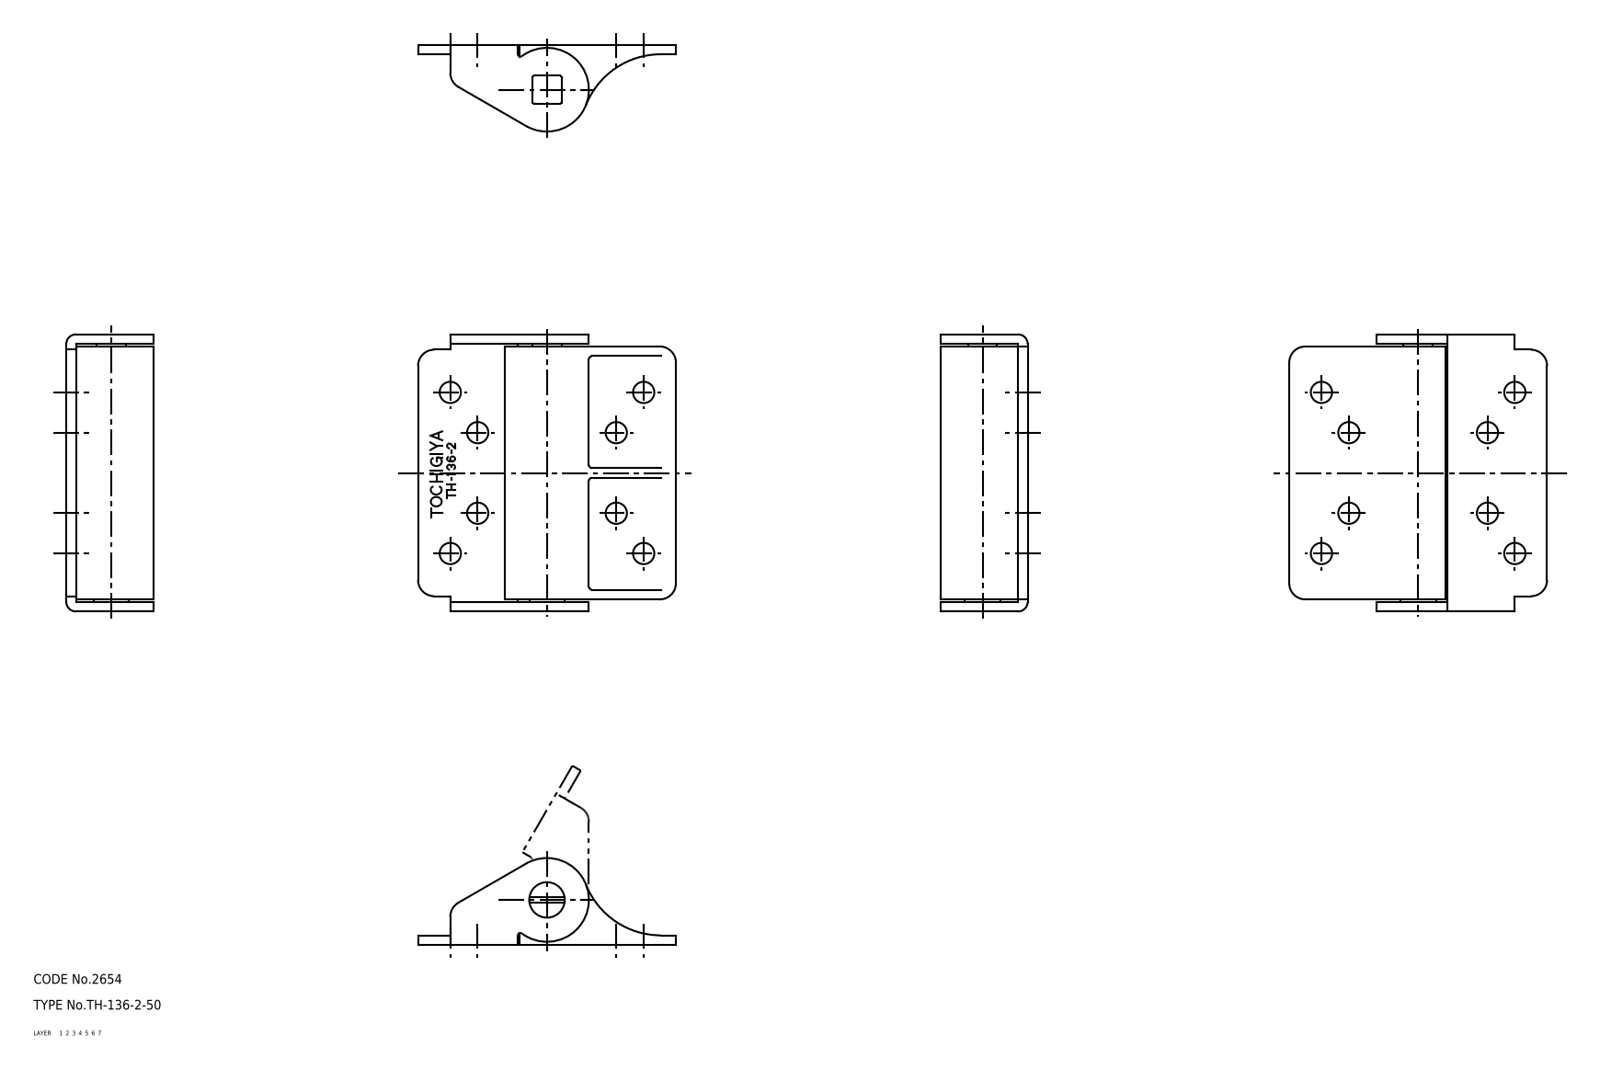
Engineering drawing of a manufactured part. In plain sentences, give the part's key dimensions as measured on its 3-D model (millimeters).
The part is named "hinge piece; needle; shaft; TH_136_2_50". Its 3-D file was written by "SolidWorks 2015 (AUTOMOTIVE_DESIGN)". It is 4 solids with 115 faces: 51 planar, 60 cylindrical and 4 other. Overall it measures 86 by 80 by 27 millimeters. Its volume is 65 690 cubic millimeters and its surface area 28 192 square millimeters. Round holes: 8 of diameter 6.6, 1 of diameter 2.5, 1 of diameter 11. Round bosses or shafts: 1 of diameter 26. Partial cylindrical surfaces (rounded edges, fillets, slot ends): 9 of radius 1, 5 of radius 5, 2 of radius 3, 1 of radius 0.75, 1 of radius 6, 1 of radius 25. The main face-to-face distances are 3, 3.75, 79.25, 82.25, 83, 0.75, 80, 86, 78.5, 21.5. The hole center spacings are 15.12, 38.45, 53, 63.71, 25, 43, 49.74, 50.
